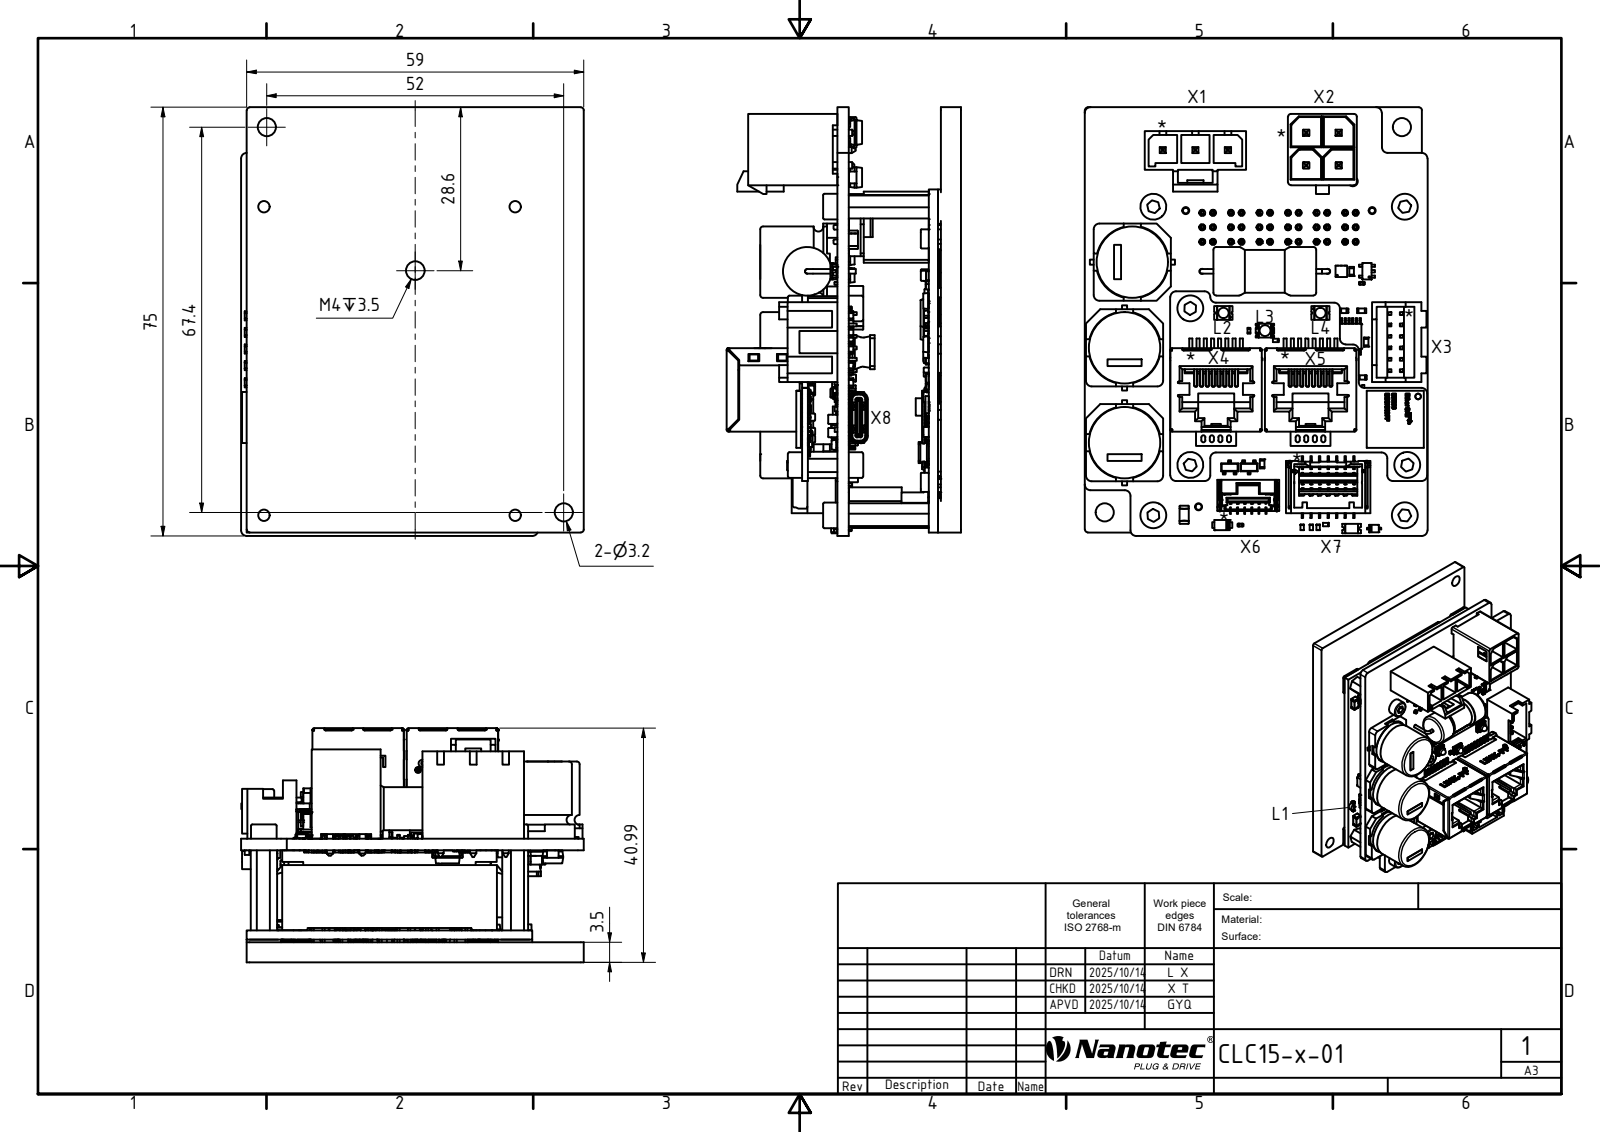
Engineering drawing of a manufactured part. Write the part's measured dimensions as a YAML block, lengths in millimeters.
part_name: "CLC15-x-01"
step_written_by: "Autodesk Inventor 2024 (AUTOMOTIVE_DESIGN)"
units: millimeters
bodies: {solids: 0, faces: 38926, planar: 24517, cylindrical: 9572, other: 4837}
overall_size: [75, 60, 40.84]
round_holes:
  - {diameter: 1.05, count: 43}
  - {diameter: 0.7, count: 12}
  - {diameter: 1.7, count: 8}
  - {diameter: 2.01, count: 7}
  - {diameter: 2.7, count: 7}
  - {diameter: 1.6, count: 6}
  - {diameter: 1.2, count: 5}
  - {diameter: 0.3, count: 4}
  - {diameter: 5.2, count: 4}
  - {diameter: 0.25, count: 3}
  - {diameter: 0.43, count: 3}
  - {diameter: 0.6, count: 3}
round_bosses_or_shafts:
  - {diameter: 4.5, count: 7}
  - {diameter: 2.5, count: 7}
  - {diameter: 1.4, count: 7}
  - {diameter: 0.4, count: 7}
  - {diameter: 1, count: 5}
  - {diameter: 0.8, count: 4}
  - {diameter: 12.5, count: 3}
  - {diameter: 3, count: 2}
partial_cylinders:
  - {radius: 0.1, count: 1605}
  - {radius: 0.12, count: 294}
  - {radius: 0.2, count: 150}
  - {radius: 1, count: 75}
  - {radius: 0.15, count: 70}
  - {radius: 0.5, count: 67}
  - {radius: 0.35, count: 47}
  - {radius: 0.3, count: 46}
face_to_face_distances: [21.64, 2.03, 19.61, 4, 0.5, 17.64, 14, 16.11, 15.61, 3.5]
hole_center_spacings: [5.61, 5, 10.32, 10, 1.88, 7.13, 3.12, 6.88]
